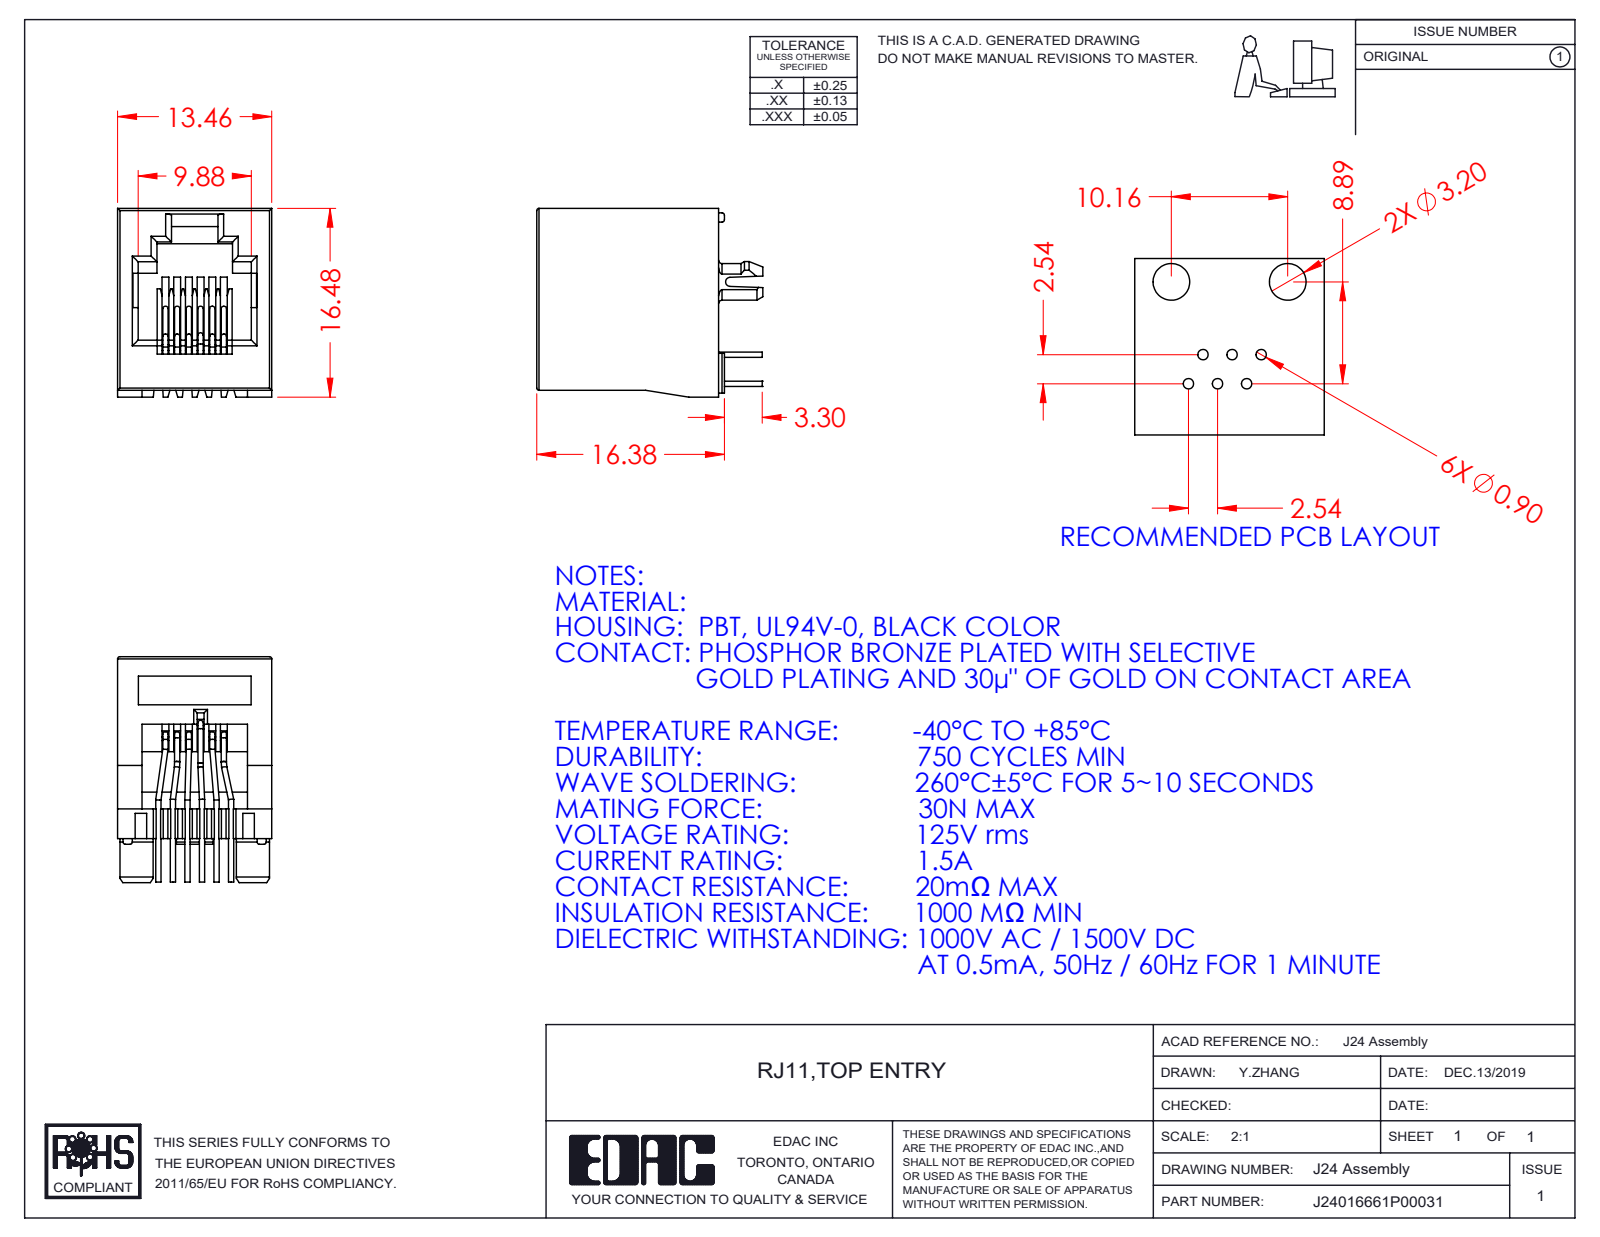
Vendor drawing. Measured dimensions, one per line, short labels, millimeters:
name: RJ24016661P00071; 24 Contacts_MBB; 24 Insulator_MBB
written by: SolidWorks 2016 (CONFIG_CONTROL_DESIGN)
unit: mm
bodies: 7 solids, 450 faces (262 planar, 152 cylindrical, 36 other)
size: 19.73 × 16.48 × 13.46
volume: 1 746 mm³; area: 2 940 mm²
holes: 6× ⌀0.46, 2× ⌀2.1
bosses: 27× ⌀0.46
rounds: 18× R0.5, 10× R0.2, 6× R0.32, 6× R0.34, 3× R0.25, 2× R1.6, 2× R1.77, 1× R0.4
face distances: 13.46, 1.02, 1.79, 11.67, 2.04, 0.6, 15.87, 8.24, 3.43, 10.03
hole spacings: 2.84, 2.54, 4.58, 5.08, 13.1, 6.84, 10.16, 10.35
